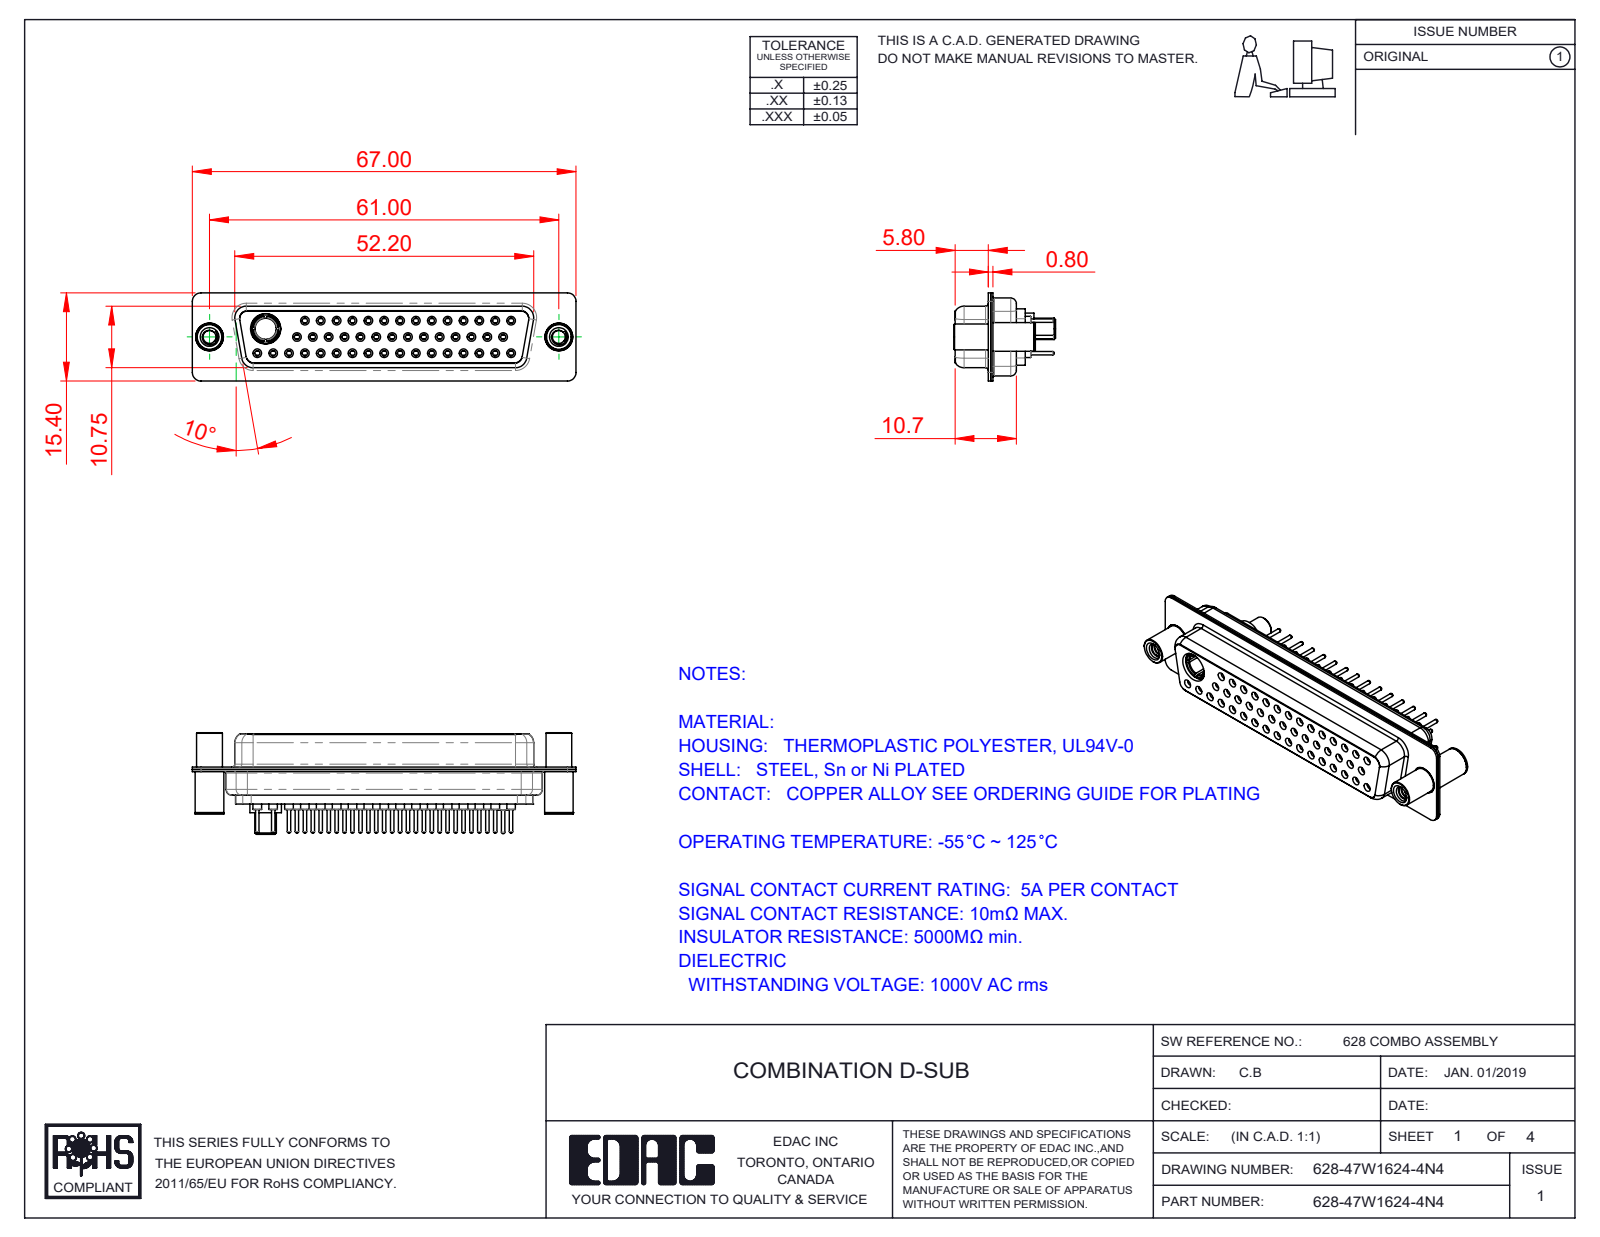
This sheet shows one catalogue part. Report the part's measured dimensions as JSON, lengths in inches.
{"part_name": "628Combo Contact Row 3_24; 628Combo Shell Rear_50 Contacts; 628Combo Threaded Standoff and Board Spacer_4; 628-47W1624-4N4 (+5 more)", "step_written_by": "SolidWorks 2016 (CONFIG_CONTROL_DESIGN)", "units": "inches", "bodies": {"solids": 53, "faces": 2957, "planar": 789, "cylindrical": 1078, "other": 1090}, "overall_size": [2.638, 0.699, 0.606], "volume_in3": 0.451, "surface_area_in2": 23.61, "round_holes": [[0.043, 46], [0.035, 45], [0.059, 45], [0.079, 45], [0.063, 31], [0.067, 14], [0.191, 3], [0.089, 2], [0.128, 2], [0.157, 2], [0.159, 2], [0.146, 1]], "round_bosses_or_shafts": [[0.087, 46], [0.024, 46], [0.063, 15], [0.197, 2], [0.195, 2], [0.189, 2], [0.177, 2], [0.217, 1]], "partial_cylinders_radius": [[0.059, 16], [0.053, 12], [0.079, 12], [0.063, 8], [0.01, 4], [0.02, 4], [0.024, 4], [0.026, 4]], "face_to_face_distances": [0.016, 0.446, 0.254, 0.238, 0.074, 0.482, 0.244, 0.228, 0.407, 0.43], "hole_center_spacings": [0.124, 0.109, 0.218, 0.327, 0.436, 0.545, 0.654, 0.763]}
